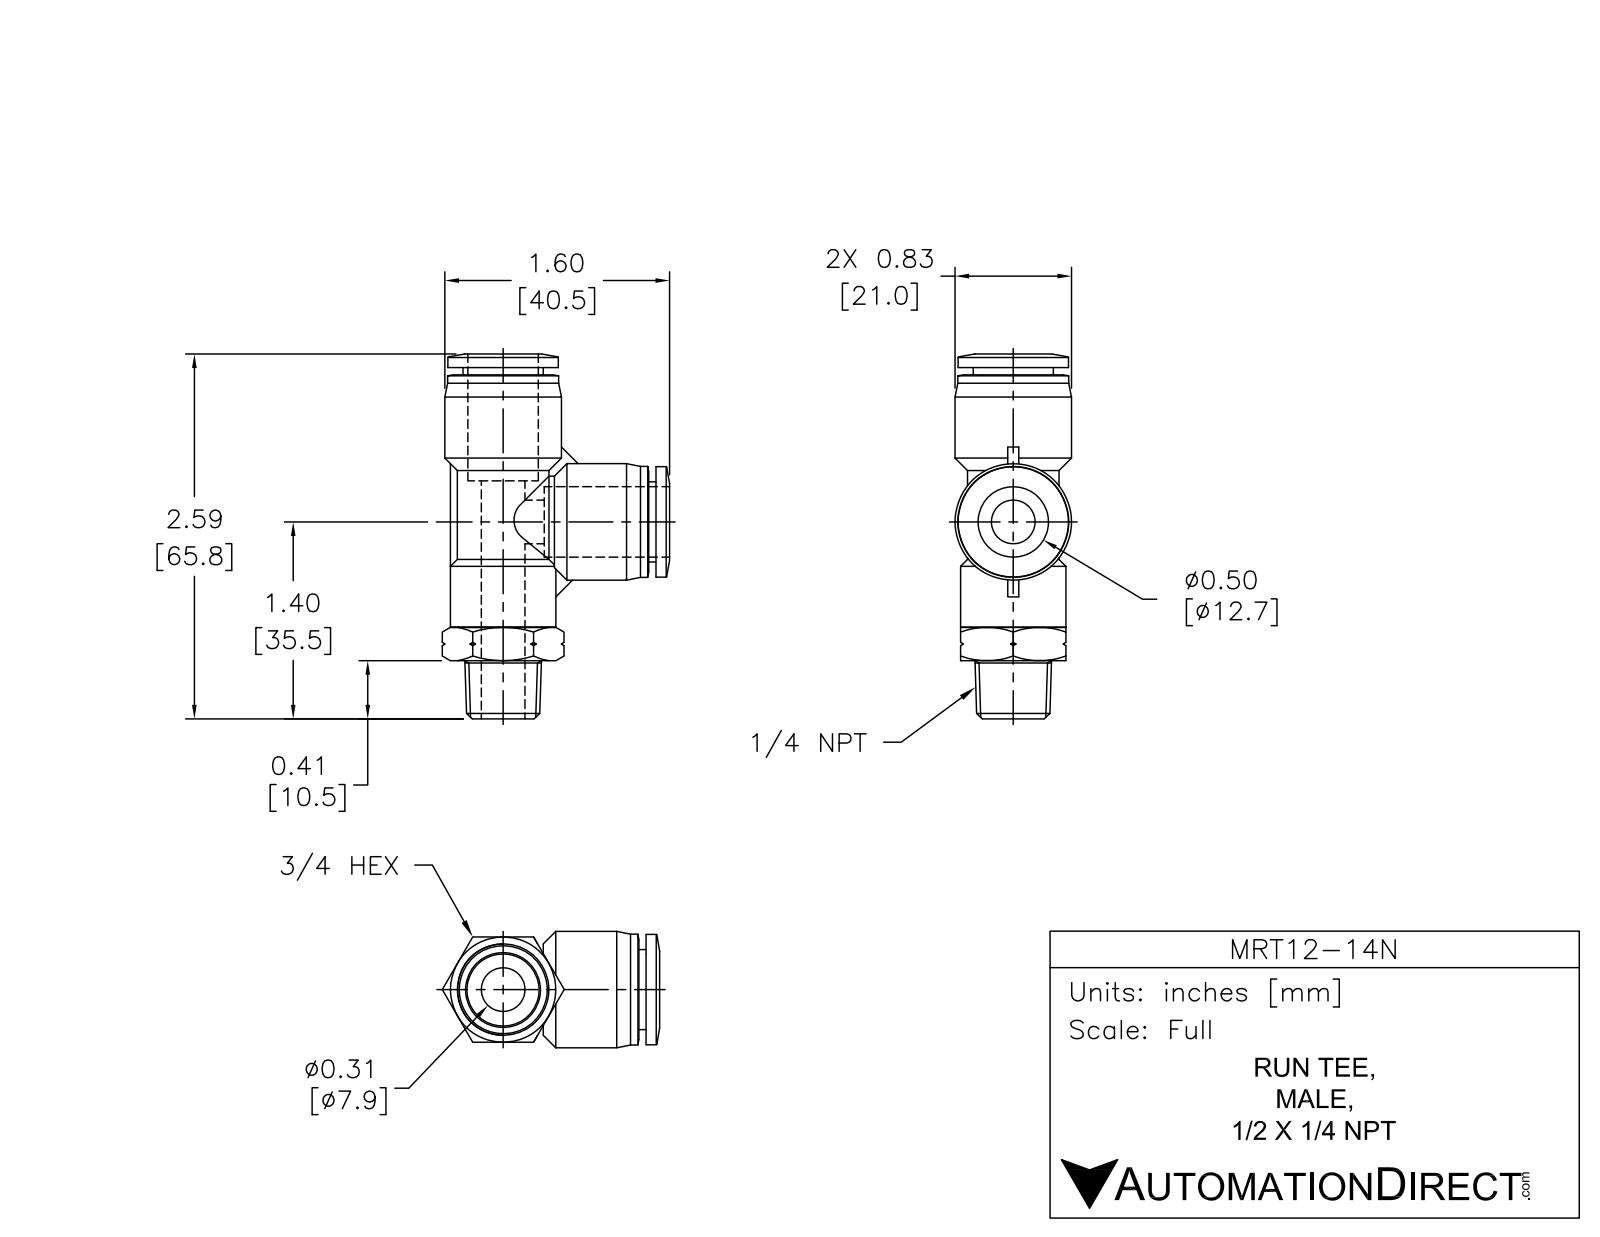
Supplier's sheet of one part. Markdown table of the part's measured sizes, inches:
| quantity | value |
| --- | --- |
| part name | MRT12-14N |
| STEP written by | SolidWorks 2015 (AUTOMOTIVE_DESIGN) |
| units | inches |
| bodies | 1 solid, 111 faces (22 planar, 31 cylindrical, 58 other) |
| overall size | 2.589 × 1.623 × 0.827 |
| volume | 0.938 in³ |
| surface area | 14.63 in² |
| round holes (diameter × count) | 0.335 × 2, 0.51 × 2 |
| round bosses / shafts (diameter × count) | 0.827 × 2, 0.787 × 2, 0.783 × 2, 0.65 × 2, 0.569 × 2, 0.748 × 1 |
| main face-to-face distances | 0.051, 0.748, 0.754, 0.805, 2.079, 0.413, 2.028, 0.335, 1.274, 1.687 |
